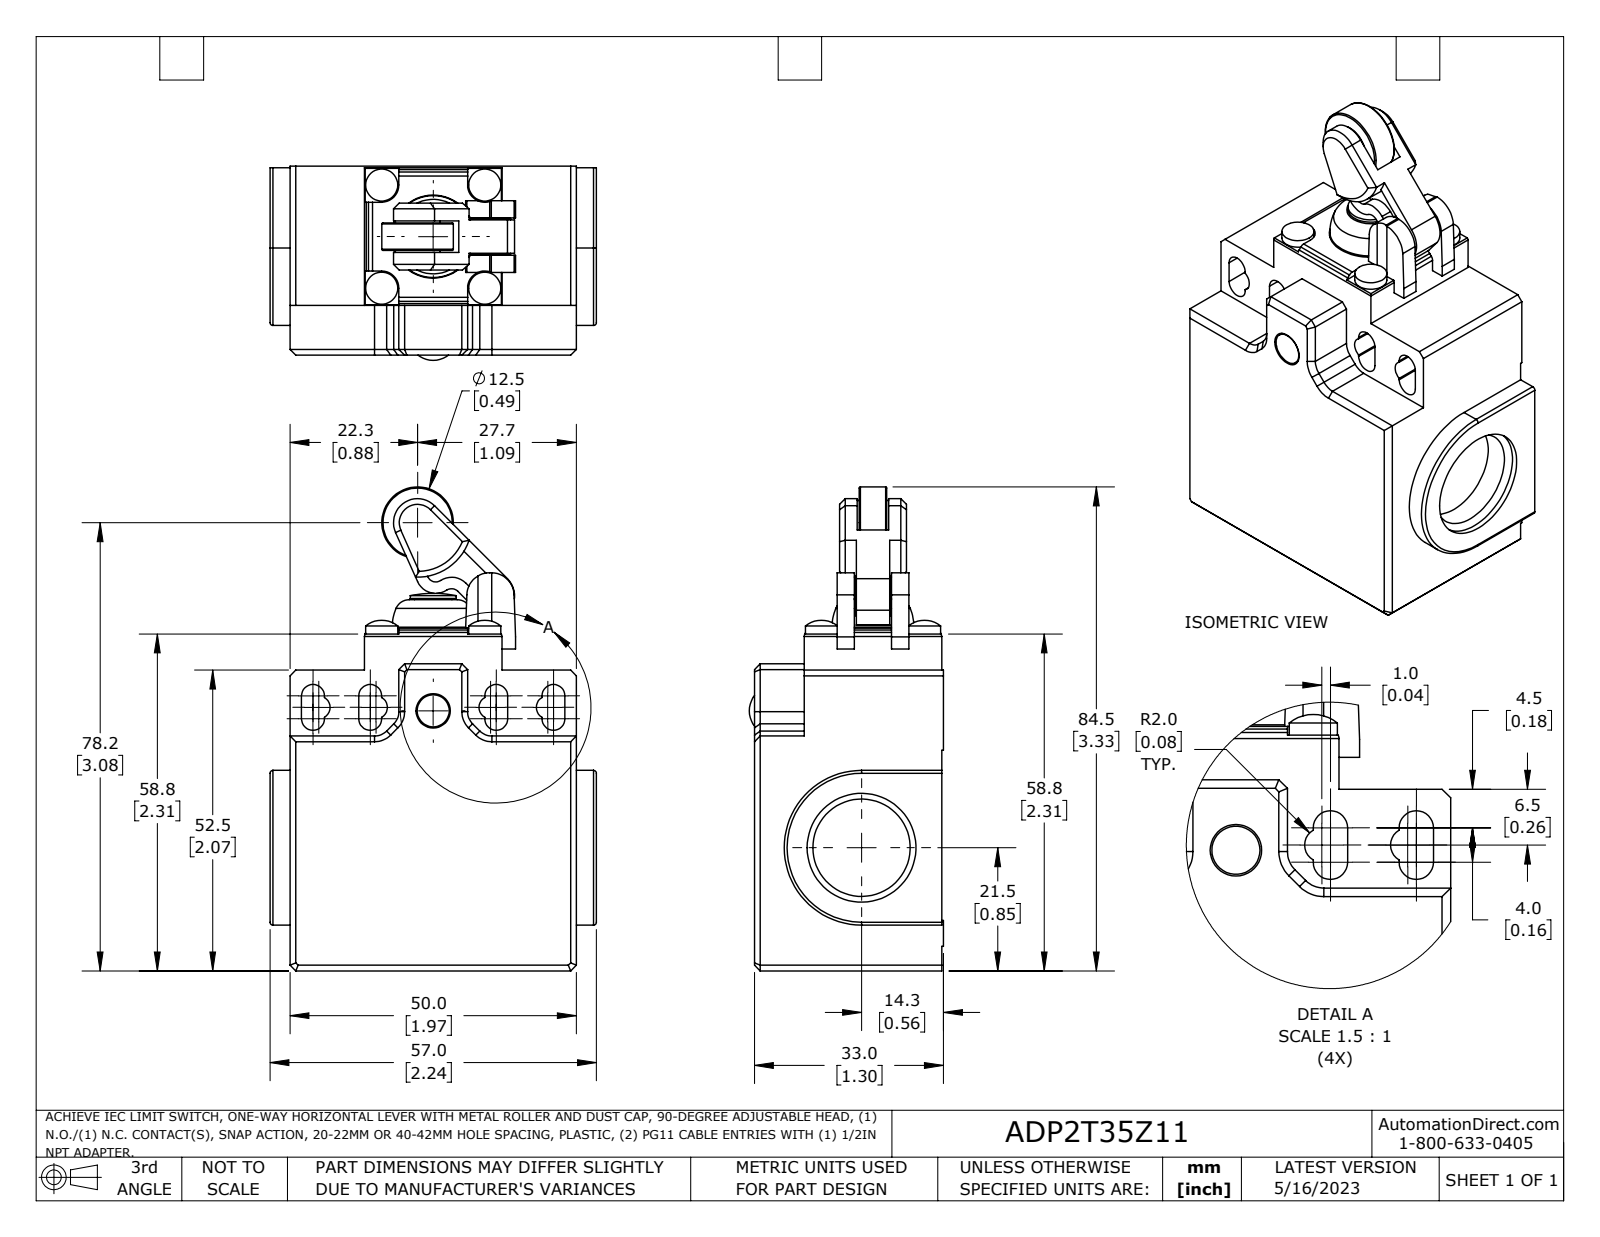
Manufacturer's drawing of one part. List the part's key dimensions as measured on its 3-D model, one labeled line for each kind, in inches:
Part name (STEP PRODUCT): ADP2T35Z11
STEP written by: SolidWorks 2021 (AUTOMOTIVE_DESIGN)
Units: inches
Bodies: 1 solid, 253 faces (149 planar, 81 cylindrical, 23 other)
Overall size (bounding box): 3.326 × 2.244 × 1.335
Volume: 5.4 in³ · Surface area: 28.47 in²
Round holes (diameter × count): ⌀0.236 ×1, ⌀0.319 ×1, ⌀0.571 ×1, ⌀0.669 ×1, ⌀0.748 ×1
Round bosses / shafts (diameter × count): ⌀0.22 ×5, ⌀0.563 ×1, ⌀0.492 ×1, ⌀0.315 ×1, ⌀0.307 ×1, ⌀0.276 ×1, ⌀0.256 ×1
Partial cylindrical surfaces — rounded edges, fillets, slot ends (radius × count): R0.079 ×12, R0.039 ×8, R0.118 ×8, R0.02 ×4, R0.059 ×2, R0.138 ×2, R0.157 ×2, R0.165 ×2
Main face-to-face distances: 1.287, 1.299, 1.969, 0.236, 0.138, 2.106, 2.067, 0.945, 1.87, 2.008
